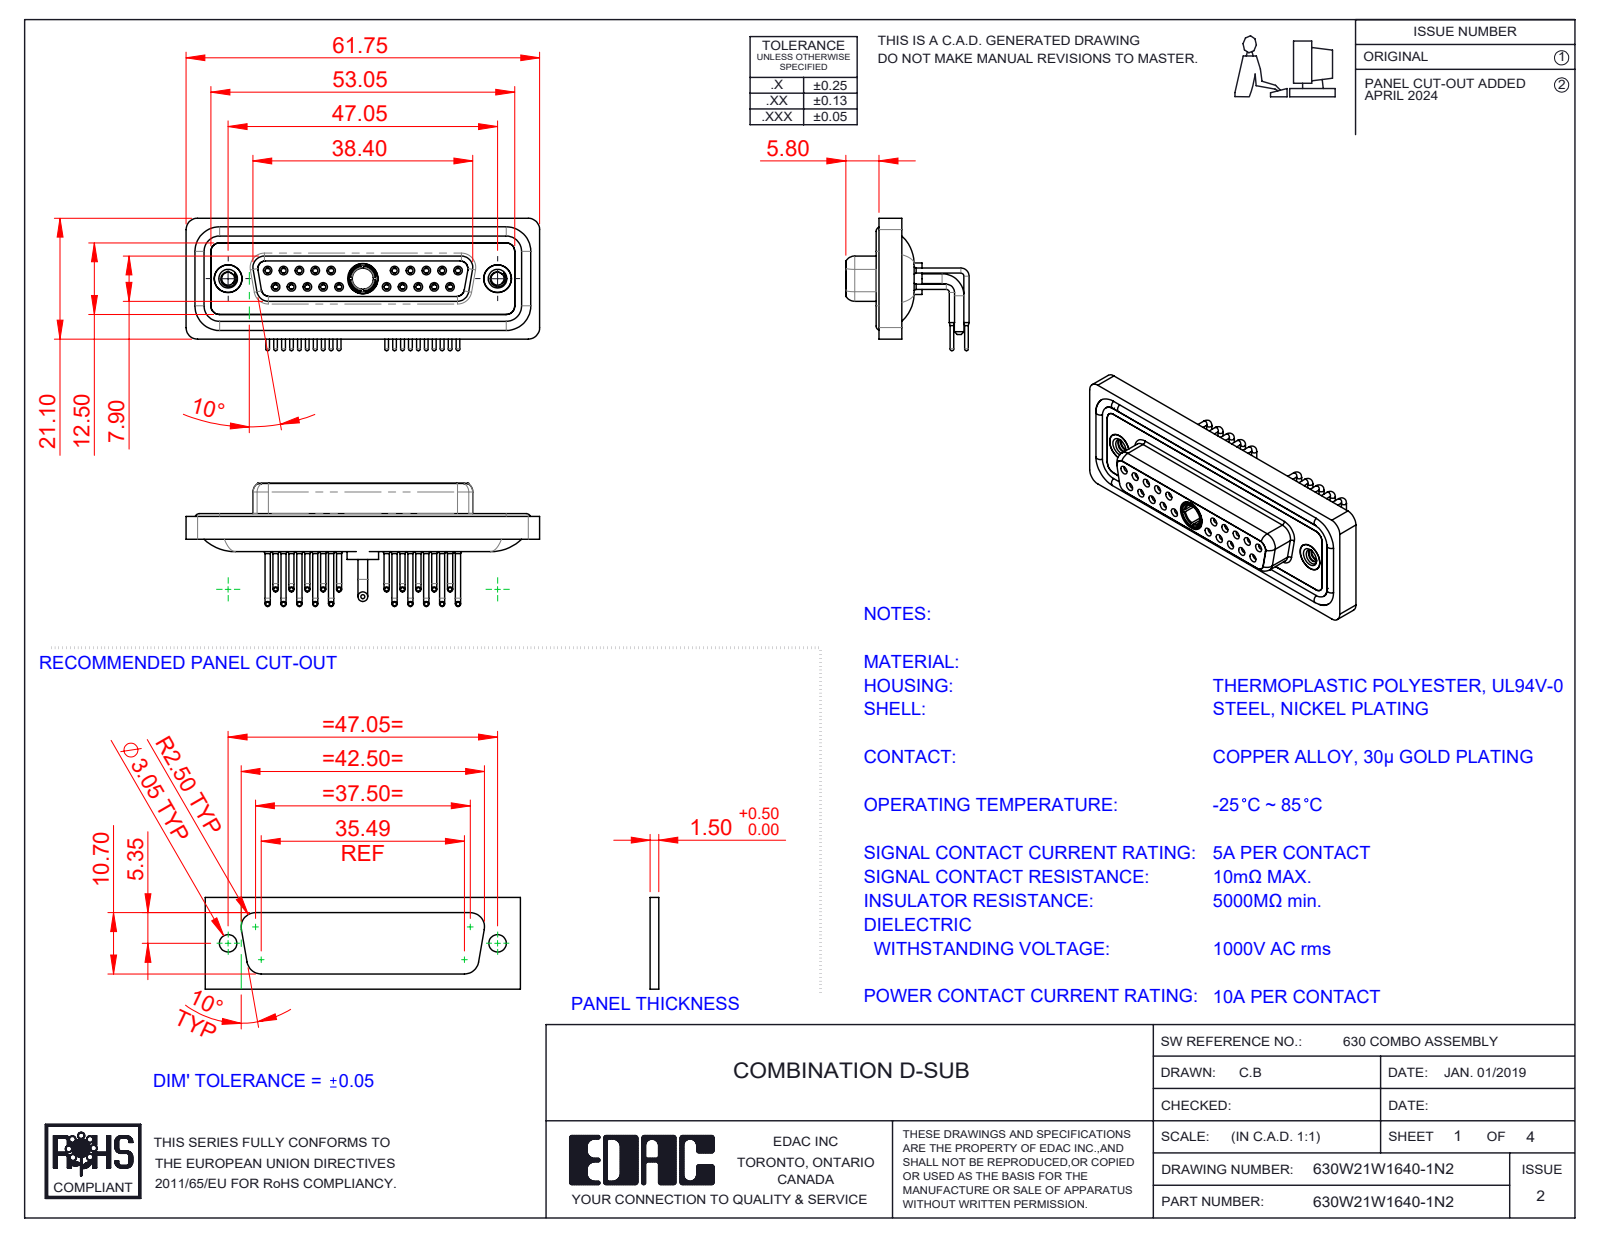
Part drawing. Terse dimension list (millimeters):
name: 630W21W1640-1N2; 630Combo Shell Front_25 Contacts; Power Socket_10A RA; 630Combo Shell Rear_25 Contacts (+5 more)
written by: SolidWorks 2023 (CONFIG_CONTROL_DESIGN)
unit: mm
bodies: 29 solids, 1524 faces (434 planar, 673 cylindrical, 417 other)
size: 61.75 × 23.12 × 21.53
volume: 8 448 mm³; area: 14 729 mm²
holes: 20× ⌀0.9, 20× ⌀1.1, 20× ⌀1.5, 20× ⌀2, 10× ⌀1.6, 10× ⌀1.7, 3× ⌀4.85, 2× ⌀2.26, 2× ⌀4, 2× ⌀4.05, 2× ⌀5, 1× ⌀3.7
bosses: 20× ⌀0.9, 20× ⌀0.65, 14× ⌀1.6, 2× ⌀4.95, 2× ⌀4.8, 2× ⌀1.7, 1× ⌀5.5, 1× ⌀5.2
rounds: 18× R1.5, 18× R2, 8× R1.35, 8× R1.6, 4× R0.25, 4× R0.5, 4× R0.6, 4× R0.65
face distances: 0.4, 1.8, 4.1, 1.6, 1.1, 2.5, 3.1, 1.5, 9.8, 0.45
hole spacings: 3.16, 2.77, 5.54, 8.31, 5.04, 19.39, 20.97, 22.16
